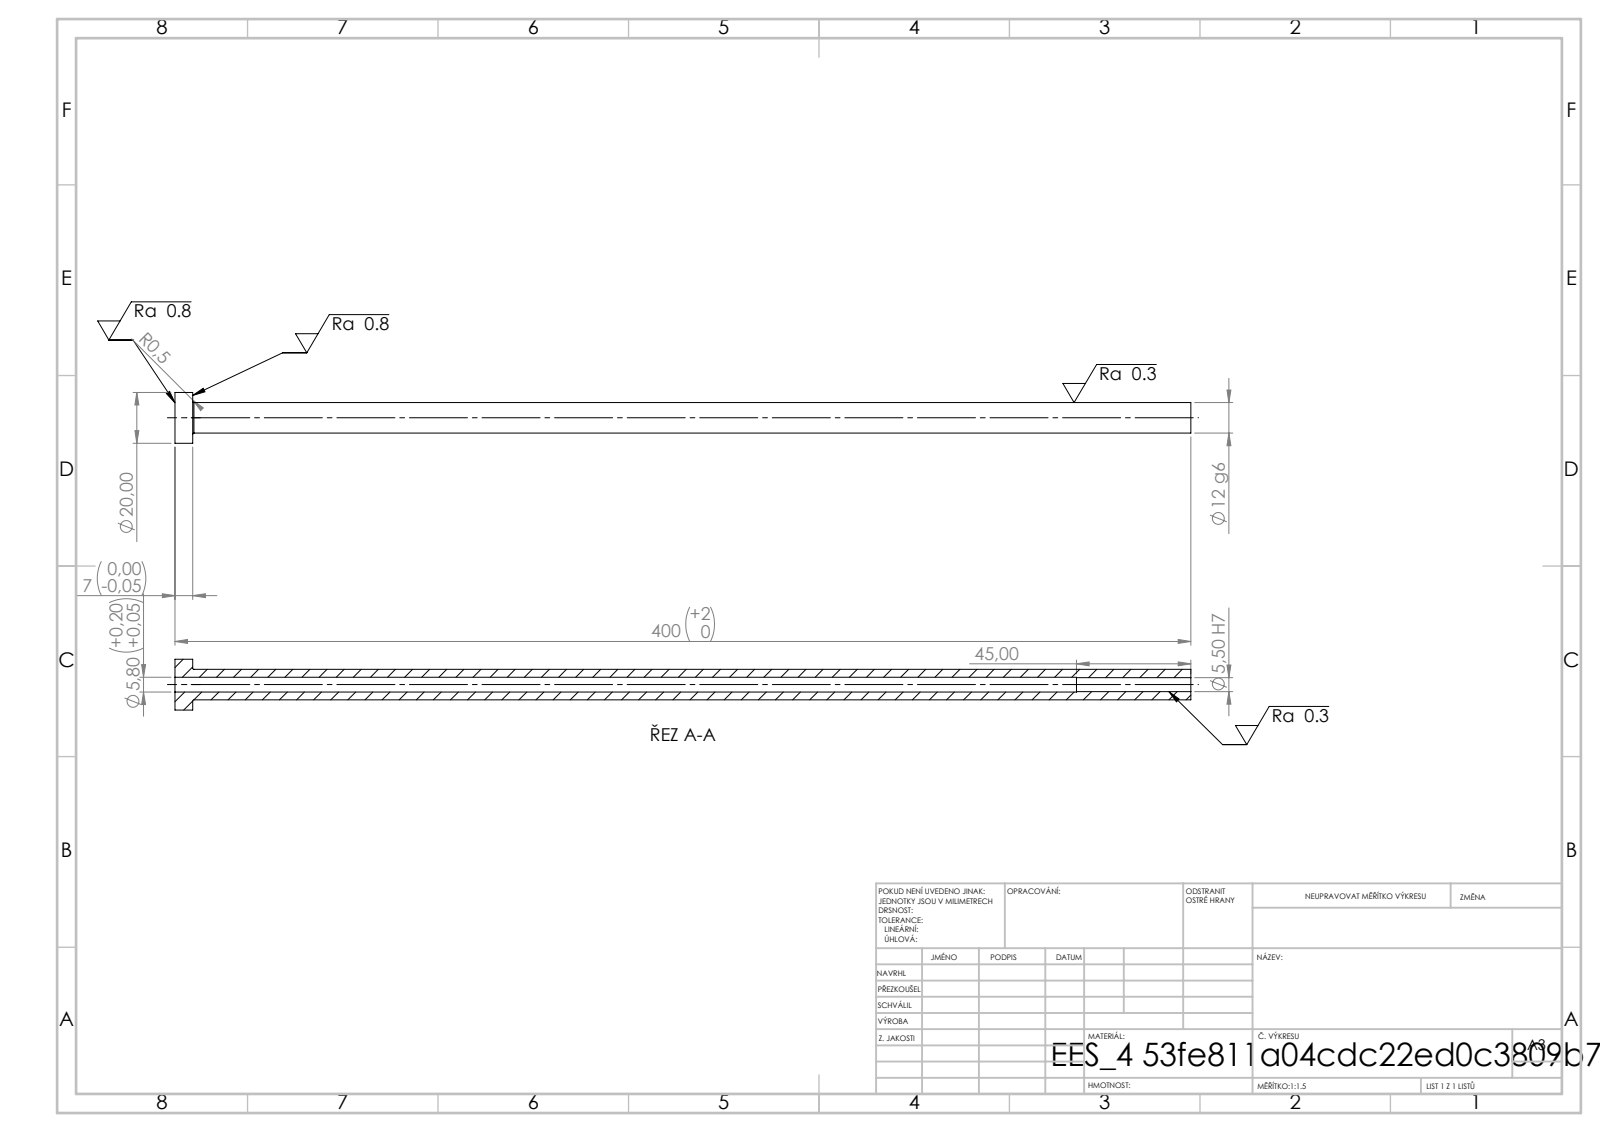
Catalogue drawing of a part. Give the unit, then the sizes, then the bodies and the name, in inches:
Units: inches
Overall size (bounding box): 15.748 × 0.787 × 0.787
Round holes (diameter × count): ⌀0.217 ×1, ⌀0.228 ×1
Round bosses / shafts (diameter × count): ⌀0.787 ×1, ⌀0.472 ×1
Main face-to-face distances: 0.276, 15.748, 15.472, 13.976, 13.701, 1.772
Volume: 2.209 in³ · Surface area: 35.76 in²
Bodies: 1 solid, 14 faces (4 planar, 8 cylindrical, 2 other)
STEP written by: SolidWorks 2019 (CONFIG_CONTROL_DESIGN)
